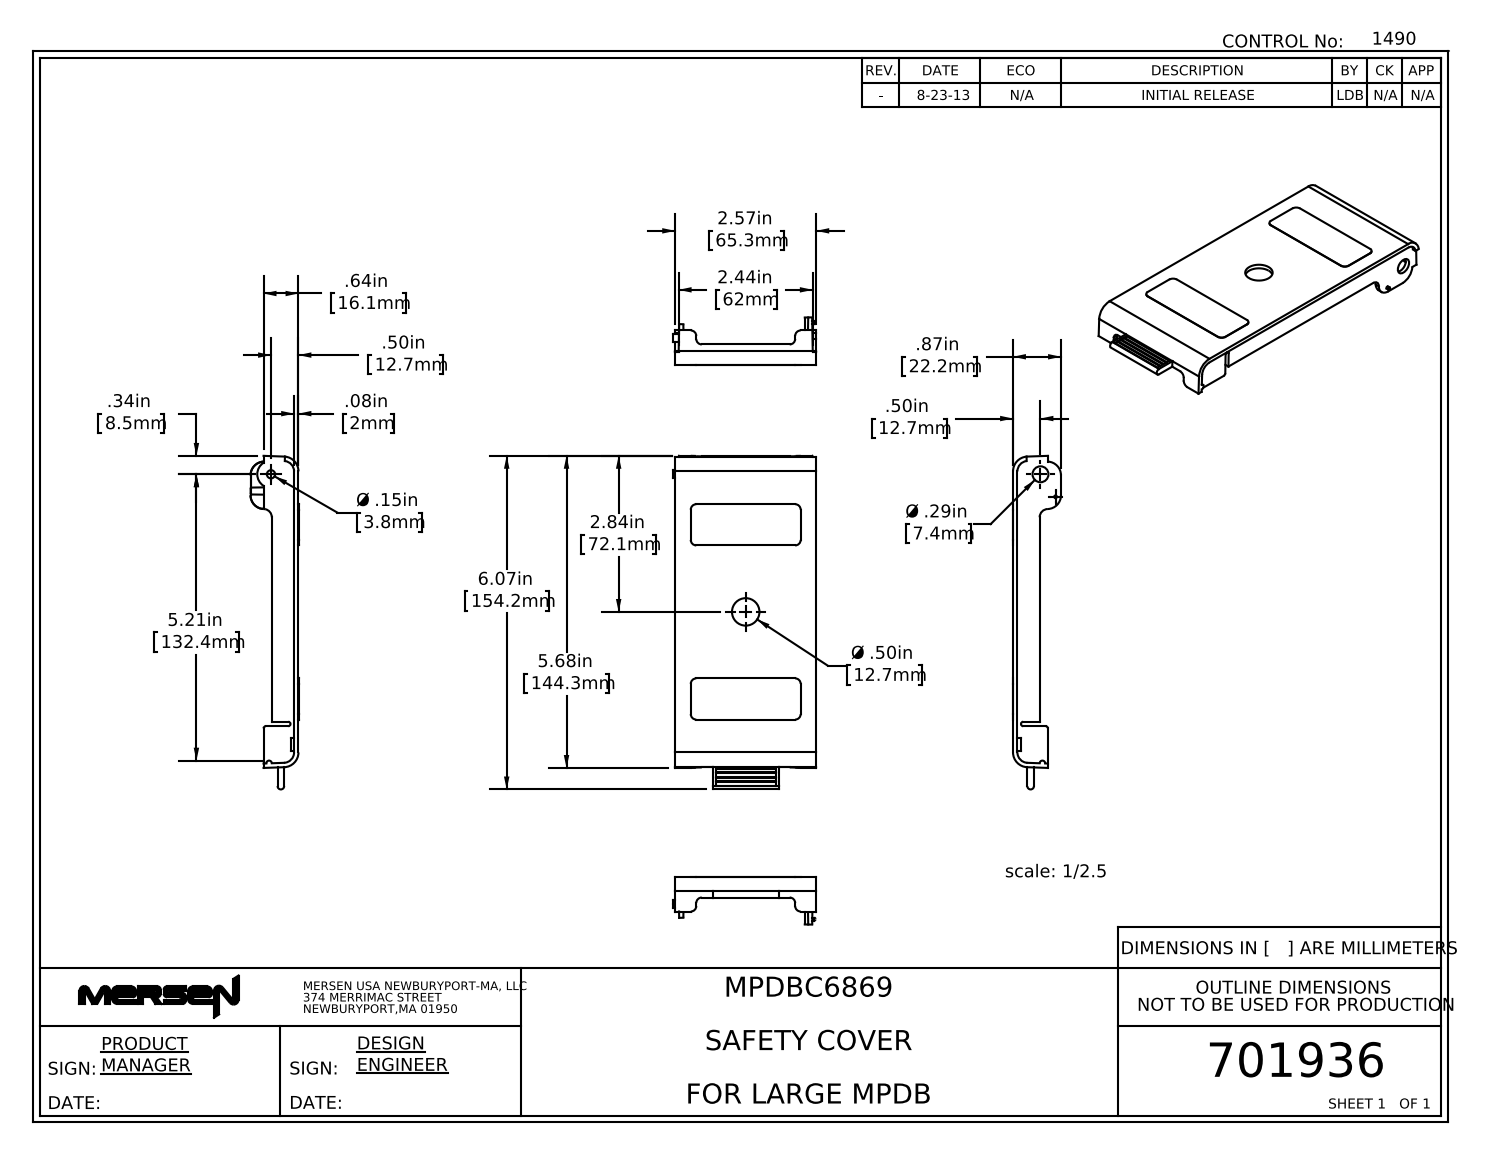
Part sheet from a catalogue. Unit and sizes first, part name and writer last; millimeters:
Units: millimetres
Overall size (bounding box): 154.2 × 66.4 × 22.2
Round holes (diameter × count): ⌀7.4 ×1, ⌀12.7 ×1
Round bosses / shafts (diameter × count): ⌀3.8 ×1, ⌀1.3 ×1
Partial cylindrical surfaces — rounded edges, fillets, slot ends (radius × count): R2.5 ×12, R0.8 ×8, R1 ×3, R6.4 ×3, R4.8 ×2, R6.9 ×2, R1.3 ×1, R1.5 ×1
Main face-to-face distances: 2, 59.6, 2.1, 10.3, 12.3, 12.3, 65.3, 2.6, 7.6, 9.7
Volume: 29 380 mm³ · Surface area: 28 940 mm²
Bodies: 2 solids, 158 faces (88 planar, 56 cylindrical, 14 other)
Part name (STEP PRODUCT): 701936rev
STEP written by: SolidWorks 2013 (AUTOMOTIVE_DESIGN)
